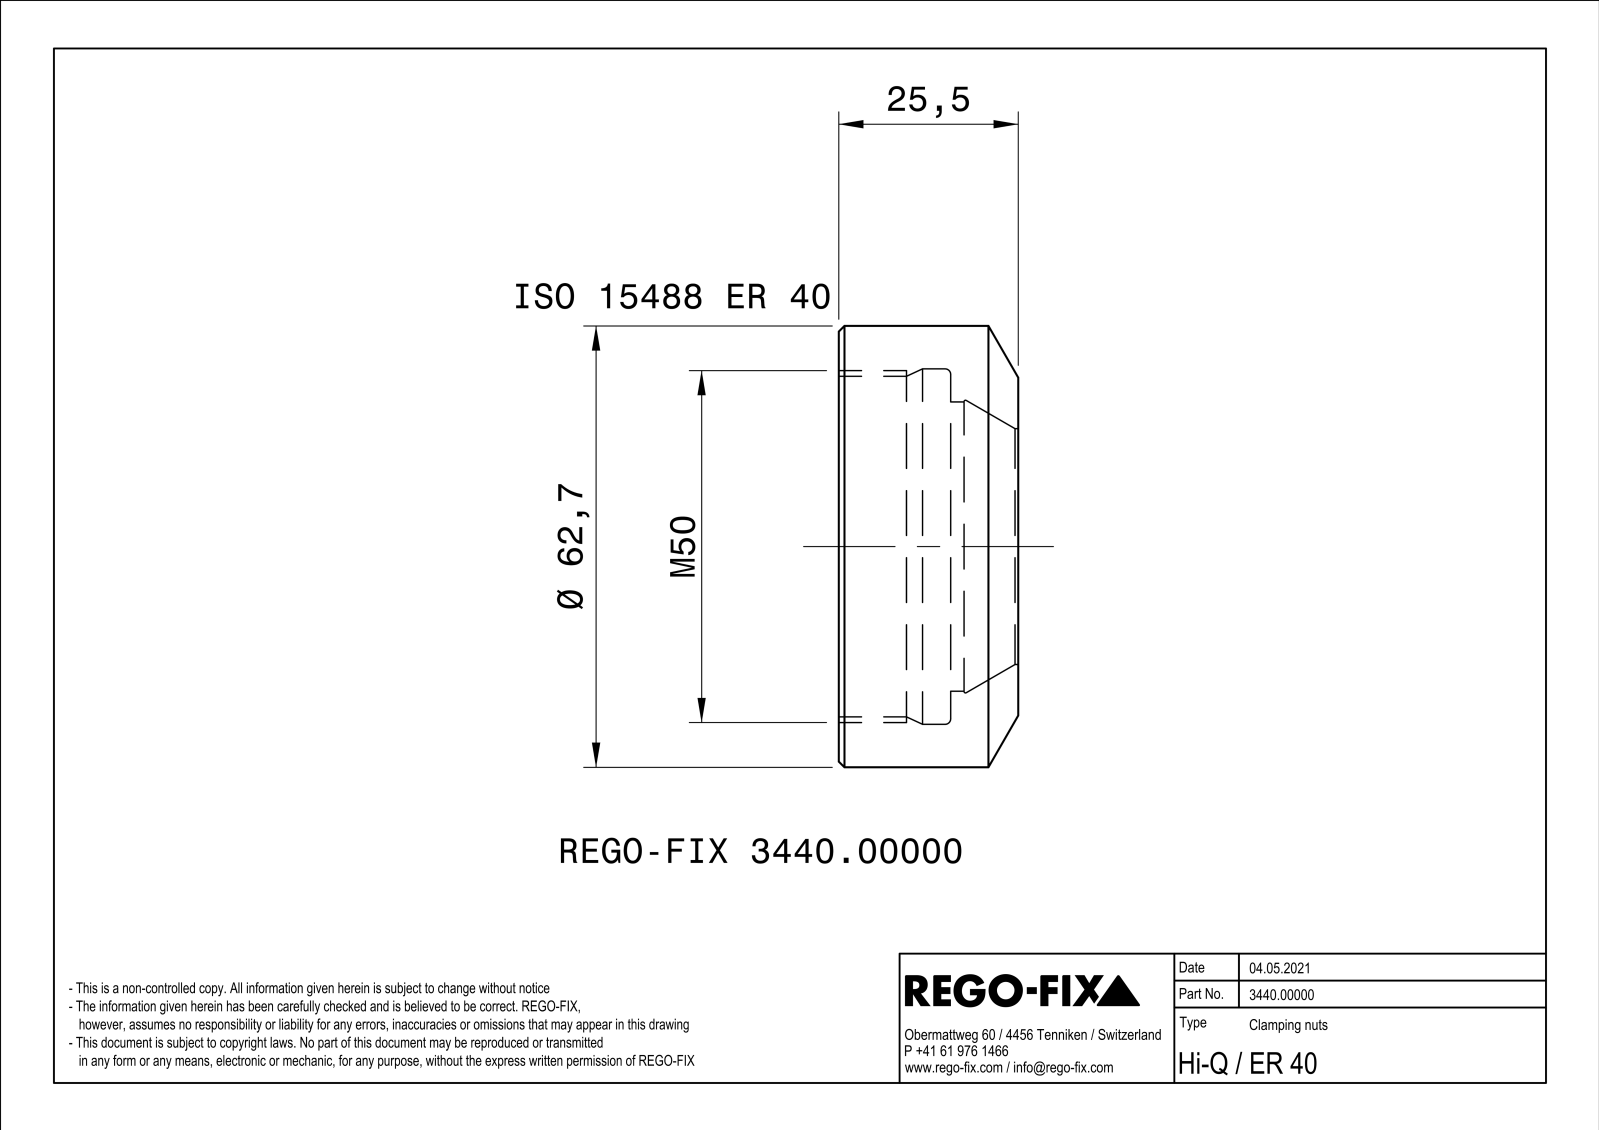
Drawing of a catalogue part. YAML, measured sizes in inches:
part_name: "NOCUT"
step_written_by: "SIEMENS PLM Software Solid Edge ST10 (AUTOMOTIVE_DESIGN)"
units: inches
bodies: {solids: 1, faces: 75, planar: 46, cylindrical: 5, other: 24}
overall_size: [2.469, 2.469, 1.004]
volume: 2.052
surface_area: 19.25
round_holes:
  - {diameter: 1.319, count: 1}
  - {diameter: 1.614, count: 1}
  - {diameter: 1.905, count: 1}
  - {diameter: 1.988, count: 1}
round_bosses_or_shafts:
  - {diameter: 2.469, count: 1}
face_to_face_distances: [1.004, 0.378, 0.626, 2.244, 0.406, 0.406, 1.688, 1.855, 1.69, 1.854]
